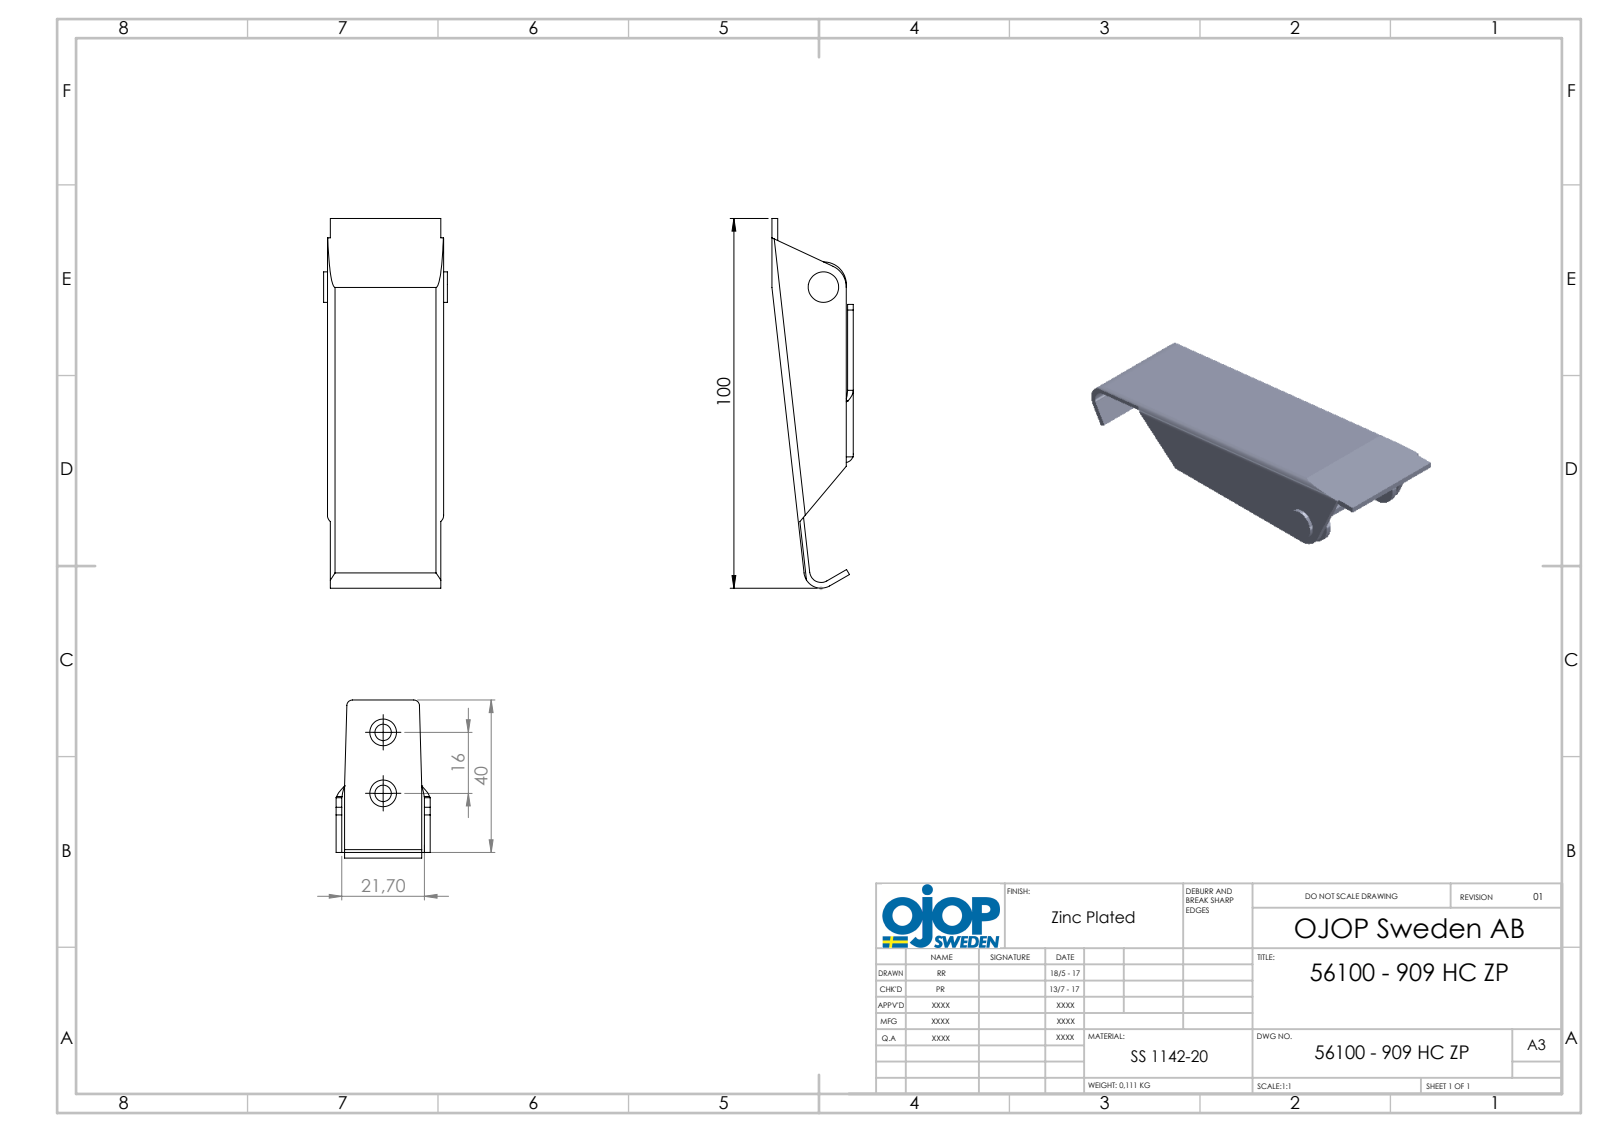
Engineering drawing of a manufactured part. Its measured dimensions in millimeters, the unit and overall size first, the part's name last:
Units: millimetres
Overall size (bounding box): 97 × 32.5 × 21.34
Round holes (diameter × count): ⌀4.3 ×2, ⌀4 ×1, ⌀4.1 ×1, ⌀5 ×1, ⌀5.3 ×1, ⌀6 ×1
Round bosses / shafts (diameter × count): ⌀10 ×1, ⌀8 ×1, ⌀7 ×1, ⌀6 ×1, ⌀3.9 ×1
Partial cylindrical surfaces — rounded edges, fillets, slot ends (radius × count): R2 ×7, R1 ×4, R0.74 ×3, R2.24 ×3, R1.5 ×2, R3 ×2, R6 ×2, R0.5 ×1
Main face-to-face distances: 1.5, 29, 19.83, 27.5, 30.5, 2.5, 27, 26.5, 24.5, 2
Hole centre spacings: 16, 39.65
Volume: 15 106 mm³ · Surface area: 18 964 mm²
Bodies: 8 solids, 175 faces (85 planar, 76 cylindrical, 14 other)
Part name (STEP PRODUCT): mellandel; underdel; överdel hake; 56100 - 909 HC ZP (+3 more)
STEP written by: SolidWorks 2015 (AUTOMOTIVE_DESIGN)
